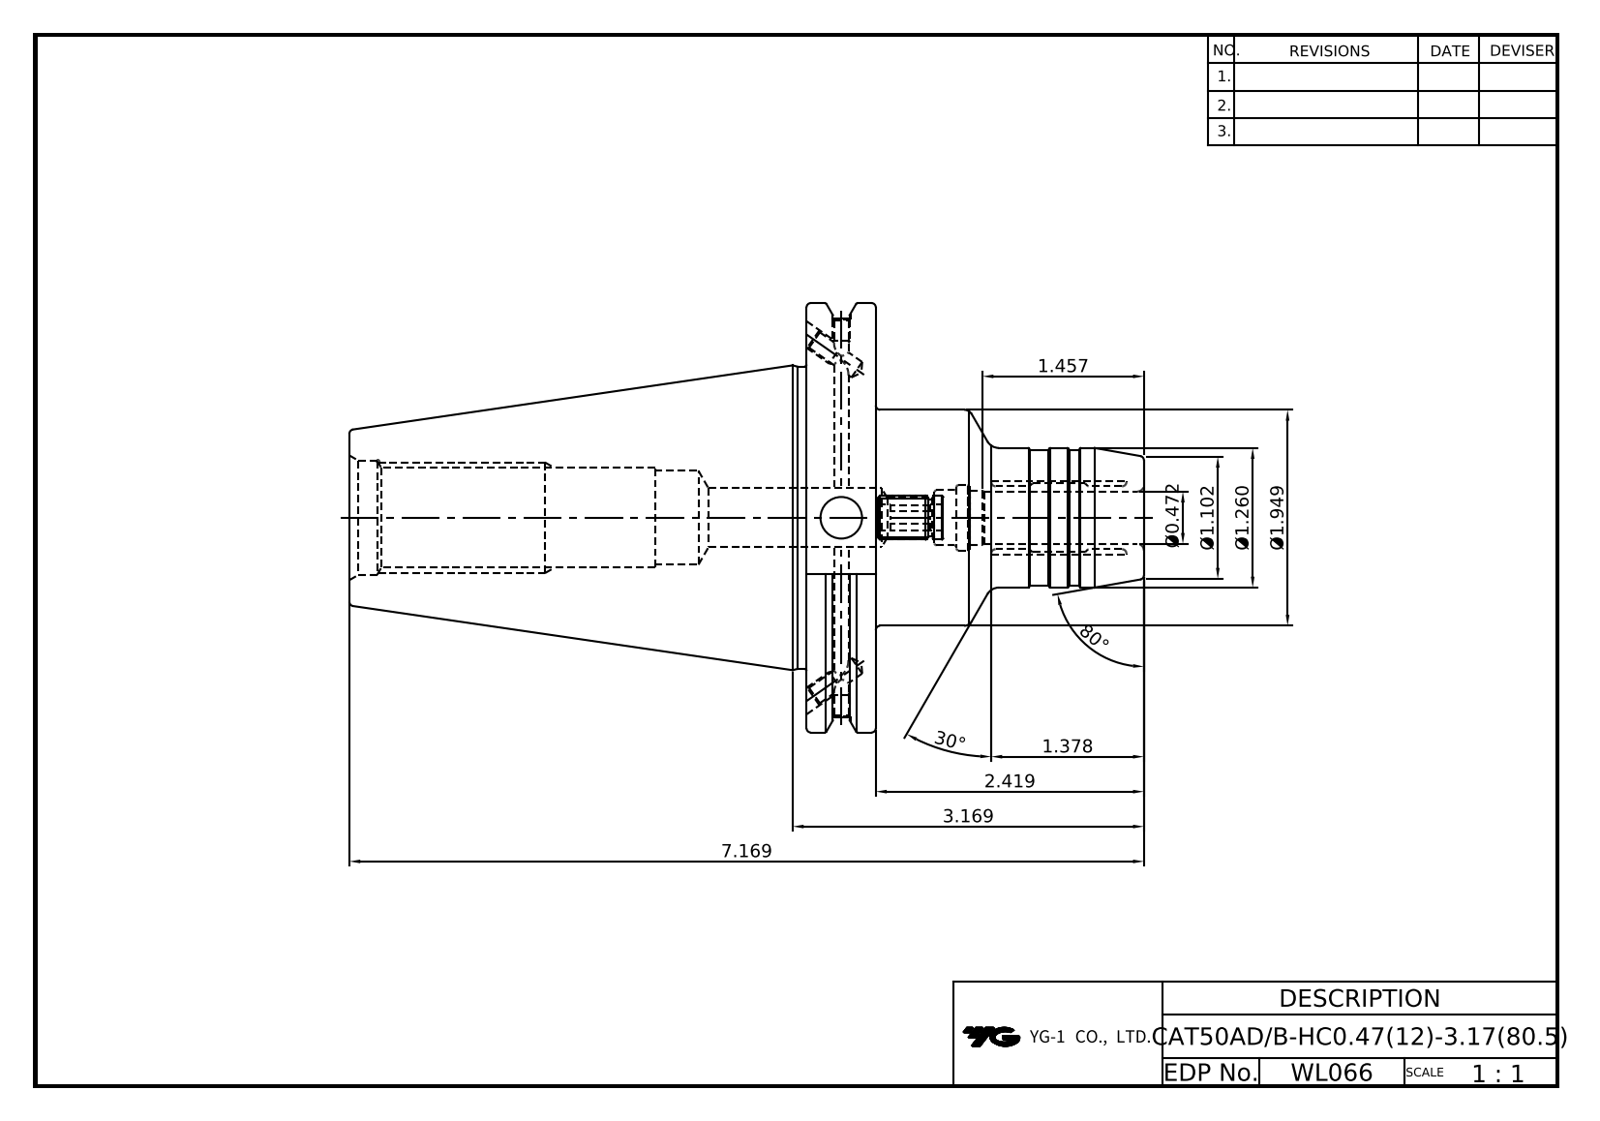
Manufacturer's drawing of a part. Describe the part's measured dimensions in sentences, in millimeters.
The part is named "LO-CAT50ADB-HC12-80.5". Its 3-D file was written by "Autodesk Inventor 2022 (AUTOMOTIVE_DESIGN)". It is 1 solid with 108 faces: 37 planar, 33 cylindrical and 38 other. Overall it measures 182.1 by 98.42 by 94.69 millimeters. Its volume is 395 829 cubic millimeters and its surface area 53 091 square millimeters. Round holes: 2 of diameter 3.24, 2 of diameter 4.13, 2 of diameter 4.2, 2 of diameter 5, 1 of diameter 8.92, 1 of diameter 9.53, 1 of diameter 12, 1 of diameter 12.6, 1 of diameter 13.5, 1 of diameter 20.5, 1 of diameter 21.97, 1 of diameter 26.2. Round bosses or shafts: 1 of diameter 98.42, 1 of diameter 91.29, 1 of diameter 69.25, 1 of diameter 49.5, 1 of diameter 32, 1 of diameter 31. The main face-to-face distances are 15.88, 104.77, 120.65, 182.1, 77.33, 61.45, 73.03, 25.9, 110.82, 6.05.
